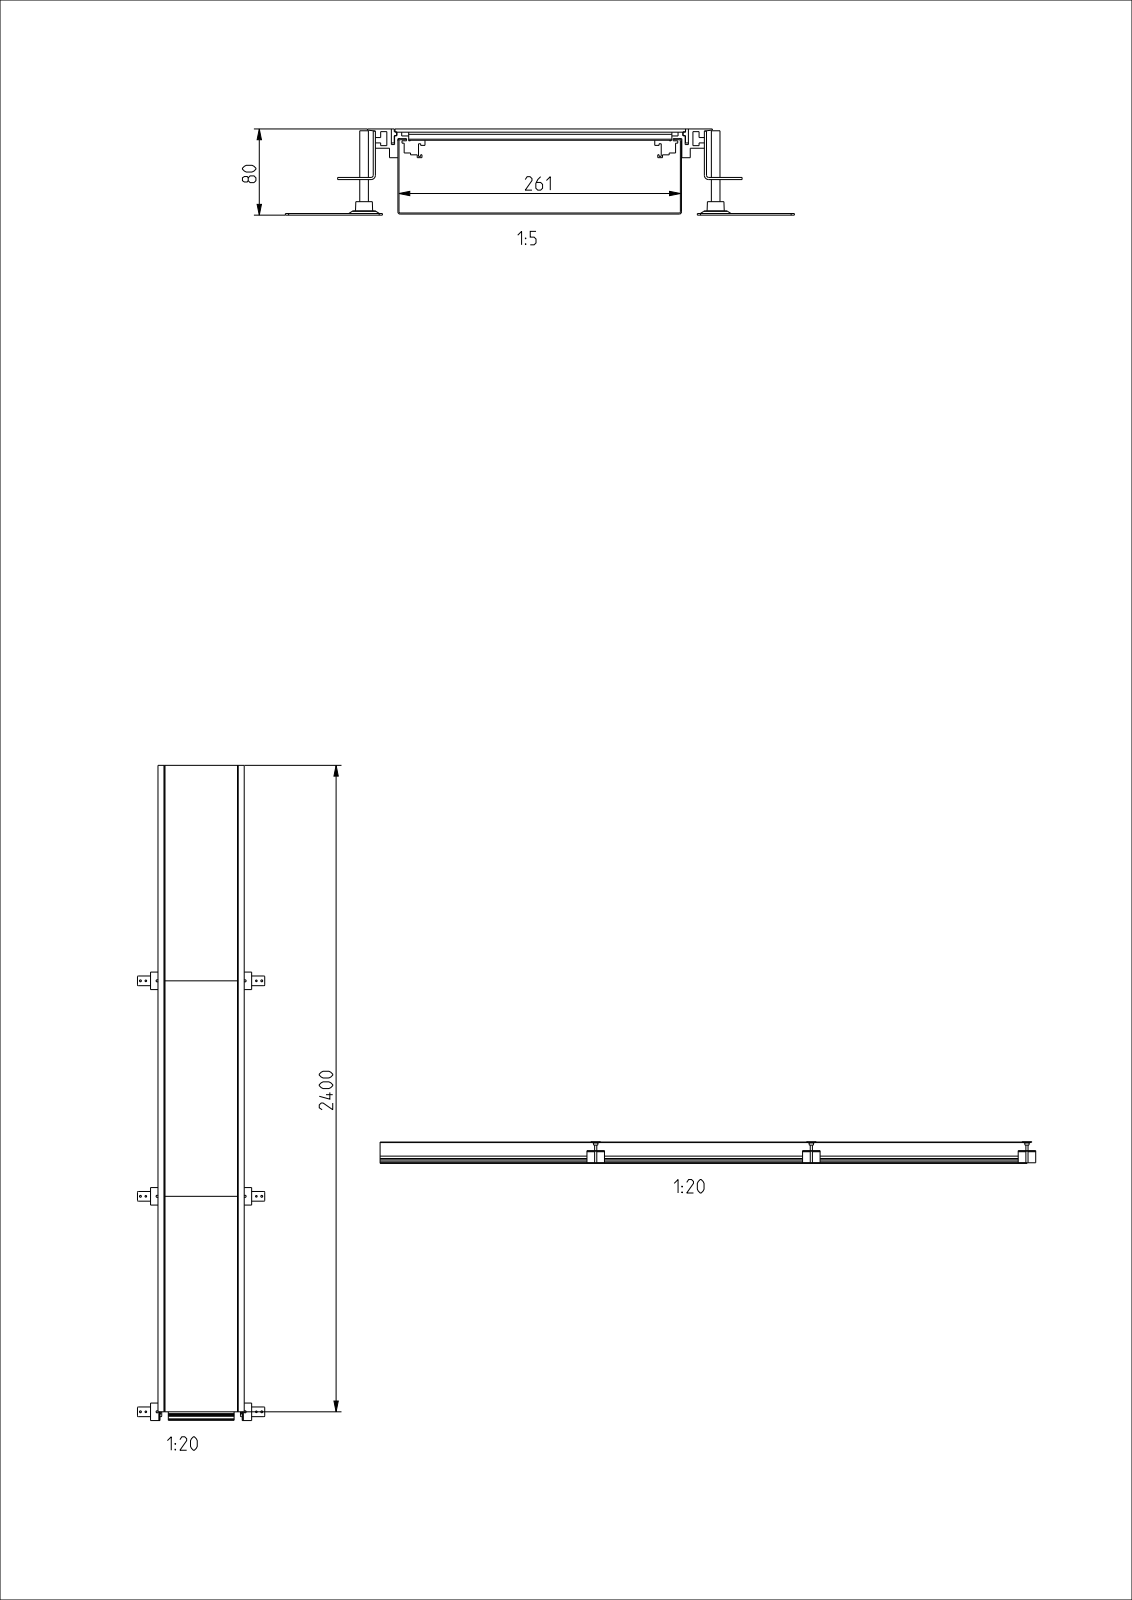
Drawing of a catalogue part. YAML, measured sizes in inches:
part_name: "U05644KUN; U05650KUN; U05985KUN; U05347KUN (+8 more)"
step_written_by: "CREO PARAMETRIC BY PTC INC, 2020281 (AUTOMOTIVE_DESIGN)"
units: inches
bodies: {solids: 40, faces: 730, planar: 480, cylindrical: 214, other: 36}
overall_size: [95.768, 18.588, 3.15]
volume: 390.1
surface_area: 8117
round_holes:
  - {diameter: 0.236, count: 6}
  - {diameter: 0.276, count: 6}
  - {diameter: 0.335, count: 6}
  - {diameter: 0.453, count: 6}
  - {diameter: 0.689, count: 6}
  - {diameter: 0.906, count: 6}
round_bosses_or_shafts:
  - {diameter: 0.787, count: 6}
  - {diameter: 0.315, count: 6}
partial_cylinders:
  - {radius: 0.079, count: 66}
  - {radius: 0.118, count: 24}
  - {radius: 0.02, count: 14}
  - {radius: 0.039, count: 4}
  - {radius: 0.157, count: 2}
face_to_face_distances: [0.039, 0.118, 2.992, 3.11, 2.953, 3.071, 10.315, 0.295, 0.256, 10.354]
hole_center_spacings: [31.496, 31.506, 31.539, 31.591, 34.671, 35.007, 35.76, 0.787]
